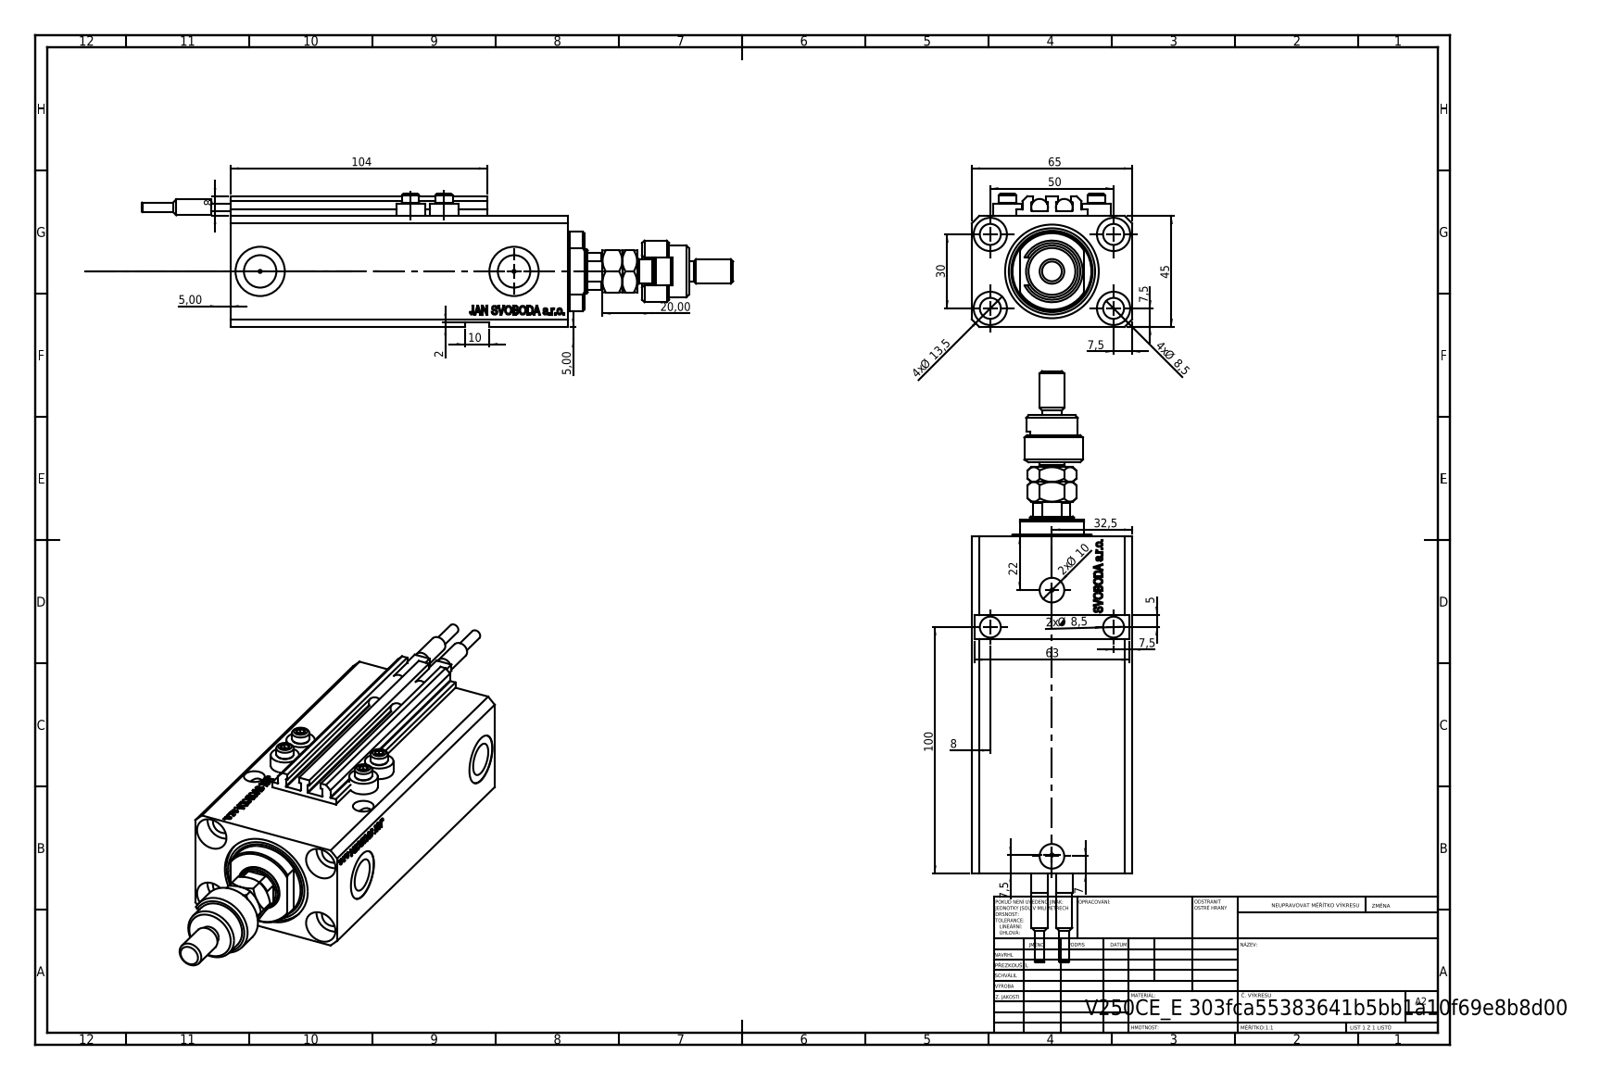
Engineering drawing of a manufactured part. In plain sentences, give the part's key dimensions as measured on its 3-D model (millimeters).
The part is named "ALLEN BOLT V250CE; V250CE_E_Body; FEMALE_PART_FOR_DFA; V250CE_VC_E (+3 more)". Its 3-D file was written by "SolidWorks 2019 (CONFIG_CONTROL_DESIGN)". It is 12 solids with 1220 faces: 575 planar, 163 cylindrical and 482 other. Overall it measures 239.9 by 65 by 54 millimeters. Its volume is 365 713 cubic millimeters and its surface area 103 938 square millimeters. Round holes: 7 of diameter 8.5, 4 of diameter 1.25, 4 of diameter 4, 4 of diameter 13.5, 2 of diameter 10, 2 of diameter 13.16, 2 of diameter 20, 1 of diameter 18, 1 of diameter 38. Round bosses or shafts: 4 of diameter 11.6, 4 of diameter 7, 2 of diameter 6.8, 2 of diameter 6.5, 2 of diameter 4, 1 of diameter 25, 1 of diameter 21, 1 of diameter 16. Partial cylindrical surfaces (rounded edges, fillets, slot ends): 10 of radius 0.2, 1 of radius 5.5, 1 of radius 8.5, 1 of radius 8.75, 1 of radius 16. The main face-to-face distances are 45, 65, 2, 47, 3, 2.5, 111.9, 10, 25.1, 20.4. The hole center spacings are 29.15, 50, 13.6, 15.12, 27.89, 30, 33.62, 36.
